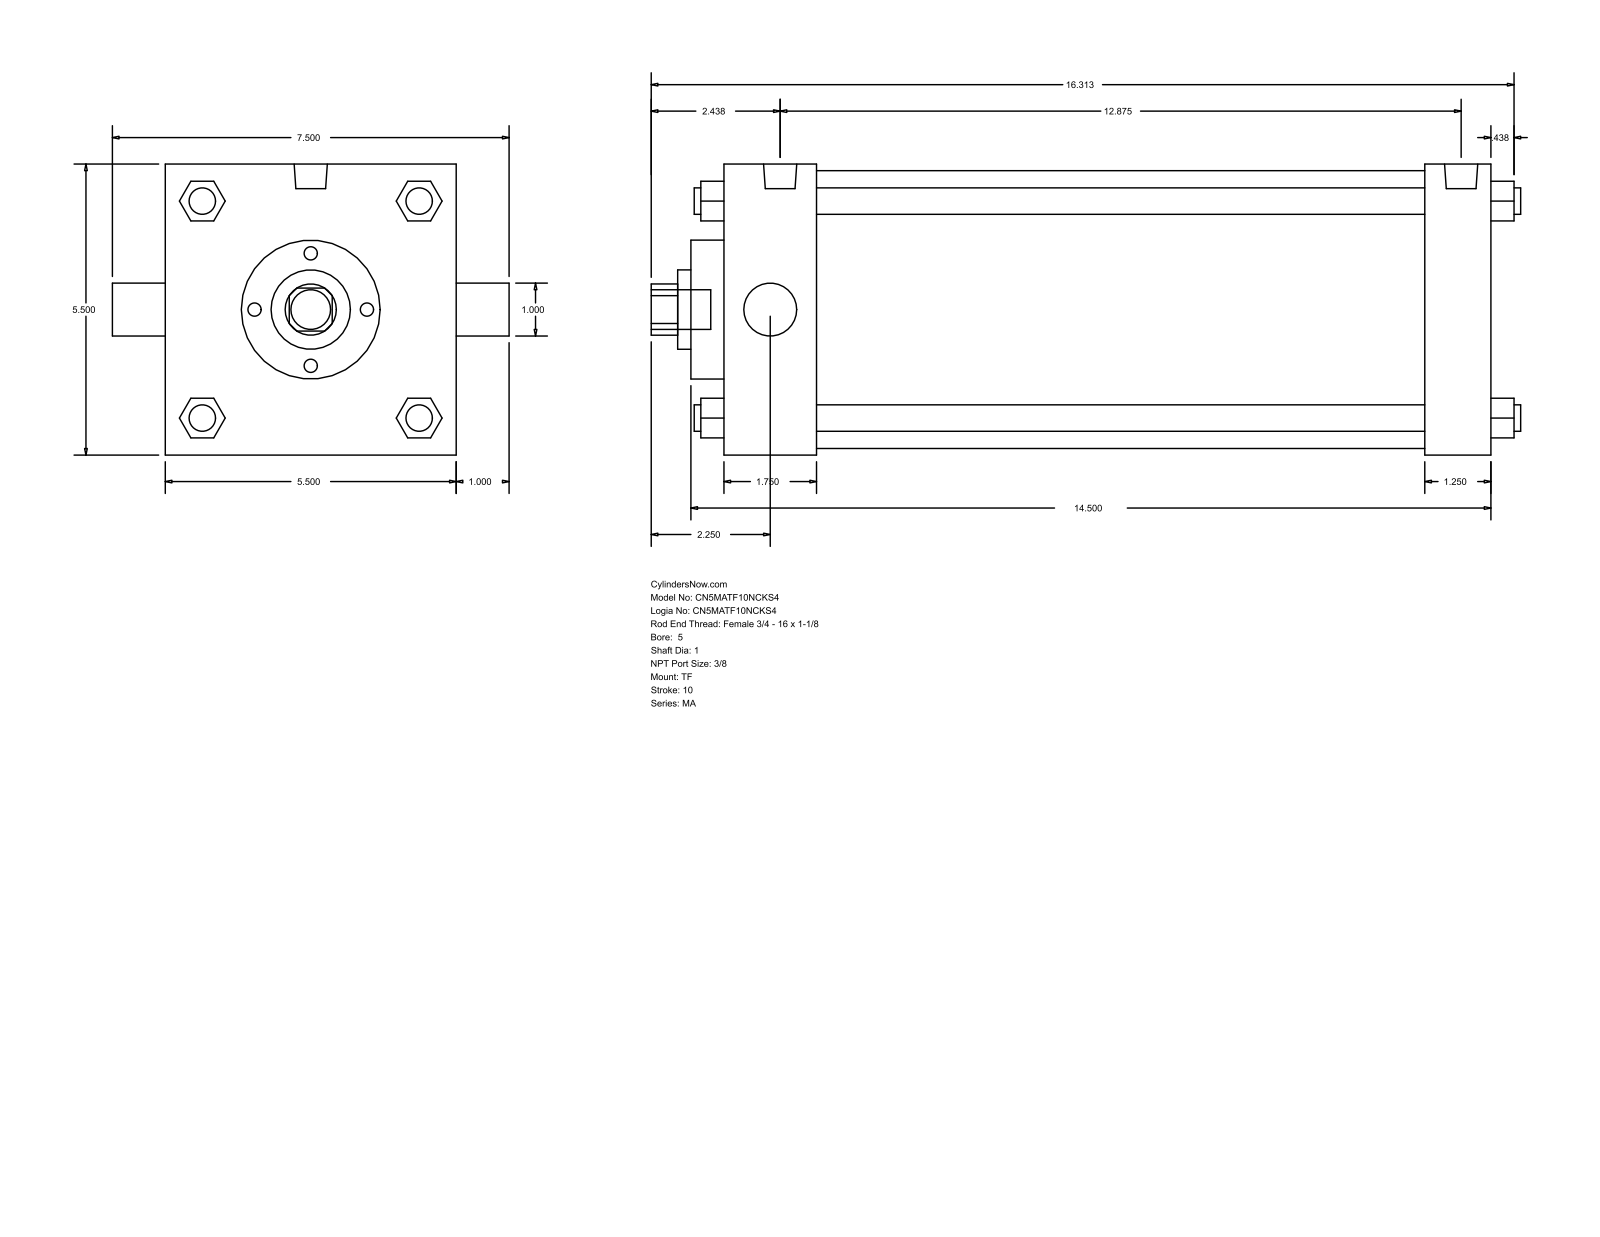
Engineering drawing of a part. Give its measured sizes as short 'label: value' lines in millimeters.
name: MA_TF__0500_1
written by: GSSL Pune (CONFIG_CONTROL_DESIGN)
unit: mm
bodies: 0 solids, 122 faces (93 planar, 29 cylindrical, 0 other)
size: 417.51 × 190.5 × 139.7
holes: 2× ⌀25.4, 1× ⌀38.1, 1× ⌀66.67, 1× ⌀133.35
bosses: 4× ⌀12.7, 3× ⌀11.11, 2× ⌀15.93, 1× ⌀19.05
rounds: 1× R12.29
face distances: 139.7, 368.31, 336.56, 31.75, 44.46, 292.1, 323.85, 15.87, 60.33, 352.43
